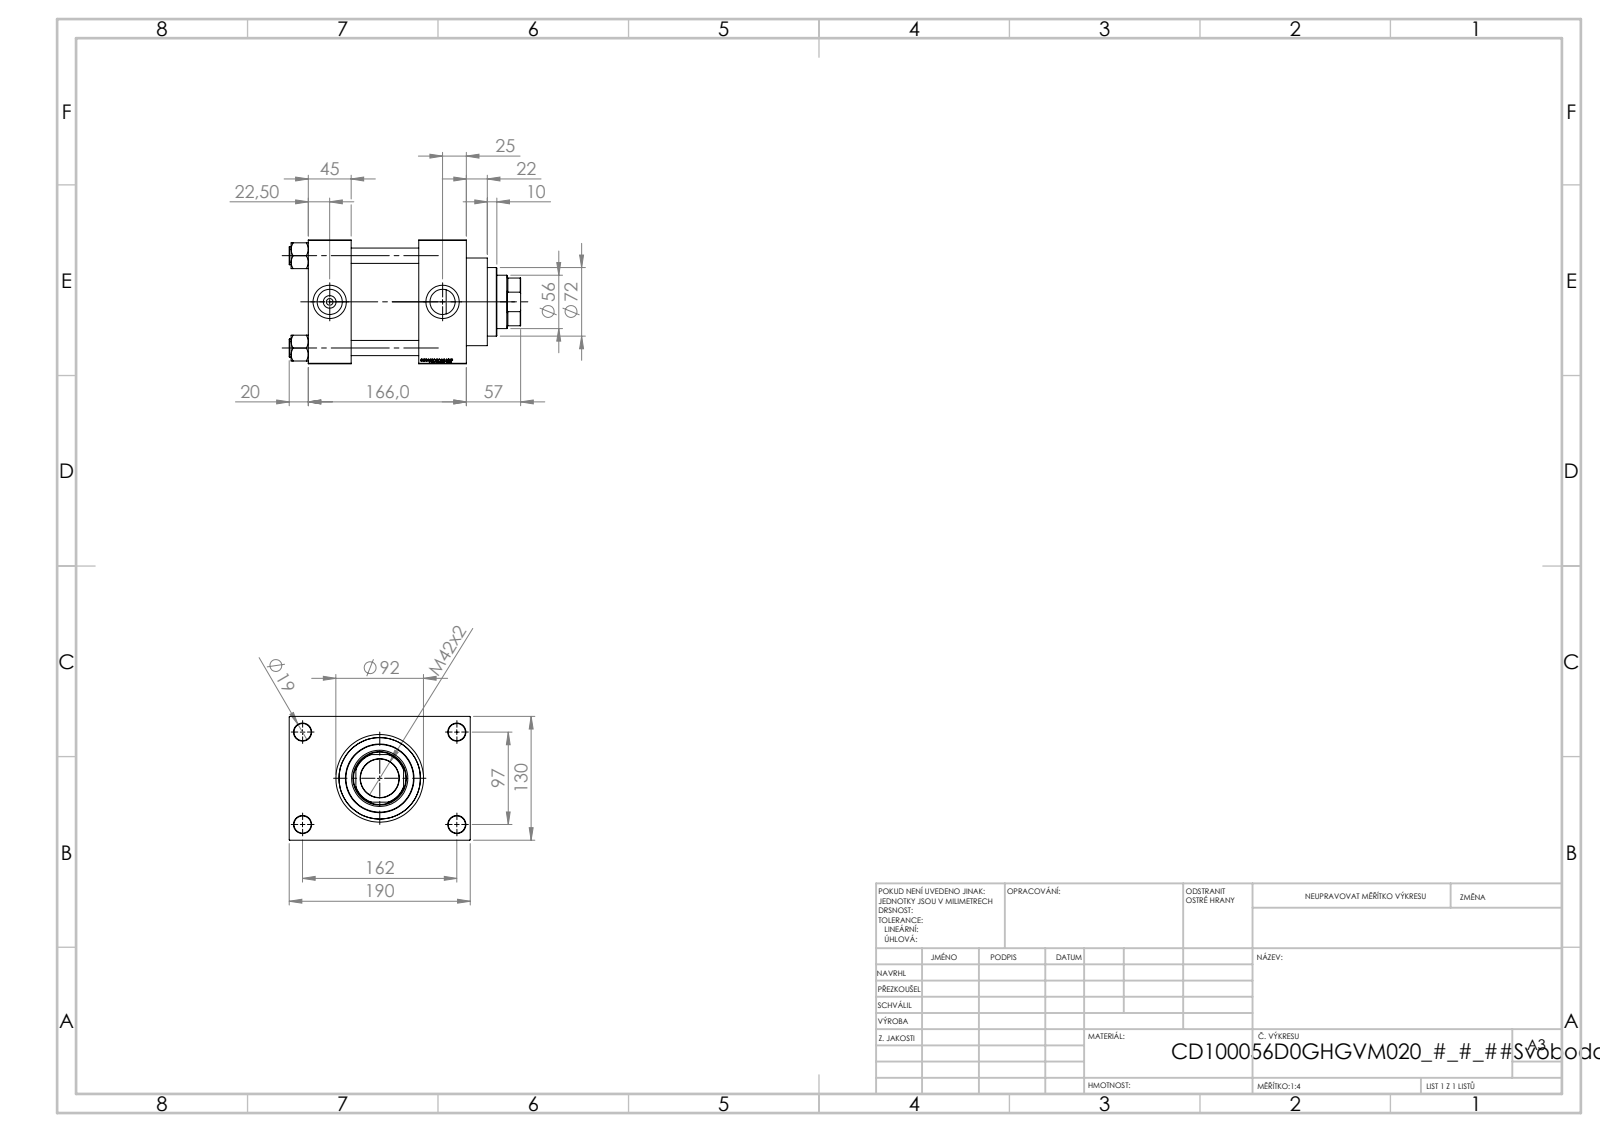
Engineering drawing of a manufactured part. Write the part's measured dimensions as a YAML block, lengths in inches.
part_name: "V215CD_NUT_M5_D; V215CD_D_Body; V215CD_VCP_D; V215CD_D_TYCINKA (+1 more)"
step_written_by: "SolidWorks 2019 (CONFIG_CONTROL_DESIGN)"
units: inches
bodies: {solids: 11, faces: 1151, planar: 545, cylindrical: 88, other: 518}
overall_size: [9.567, 7.48, 5.118]
volume: 160.4
surface_area: 561.7
round_holes:
  - {diameter: 0.63, count: 4}
  - {diameter: 0.709, count: 4}
  - {diameter: 0.276, count: 2}
  - {diameter: 1.041, count: 2}
  - {diameter: 1.378, count: 2}
  - {diameter: 1.594, count: 1}
  - {diameter: 2.205, count: 1}
  - {diameter: 2.323, count: 1}
  - {diameter: 2.992, count: 1}
  - {diameter: 3.366, count: 1}
  - {diameter: 3.937, count: 1}
round_bosses_or_shafts:
  - {diameter: 0.748, count: 4}
  - {diameter: 4.173, count: 1}
  - {diameter: 3.622, count: 1}
  - {diameter: 2.835, count: 1}
partial_cylinders:
  - {radius: 1.063, count: 1}
face_to_face_distances: [5.118, 4.567, 1.969, 1.772, 2.795, 6.535, 4.764, 1.181, 6.299, 0.787]
hole_center_spacings: [1.281, 2.698, 3.717, 3.815, 4.026, 5.096, 6.367, 3.819]
